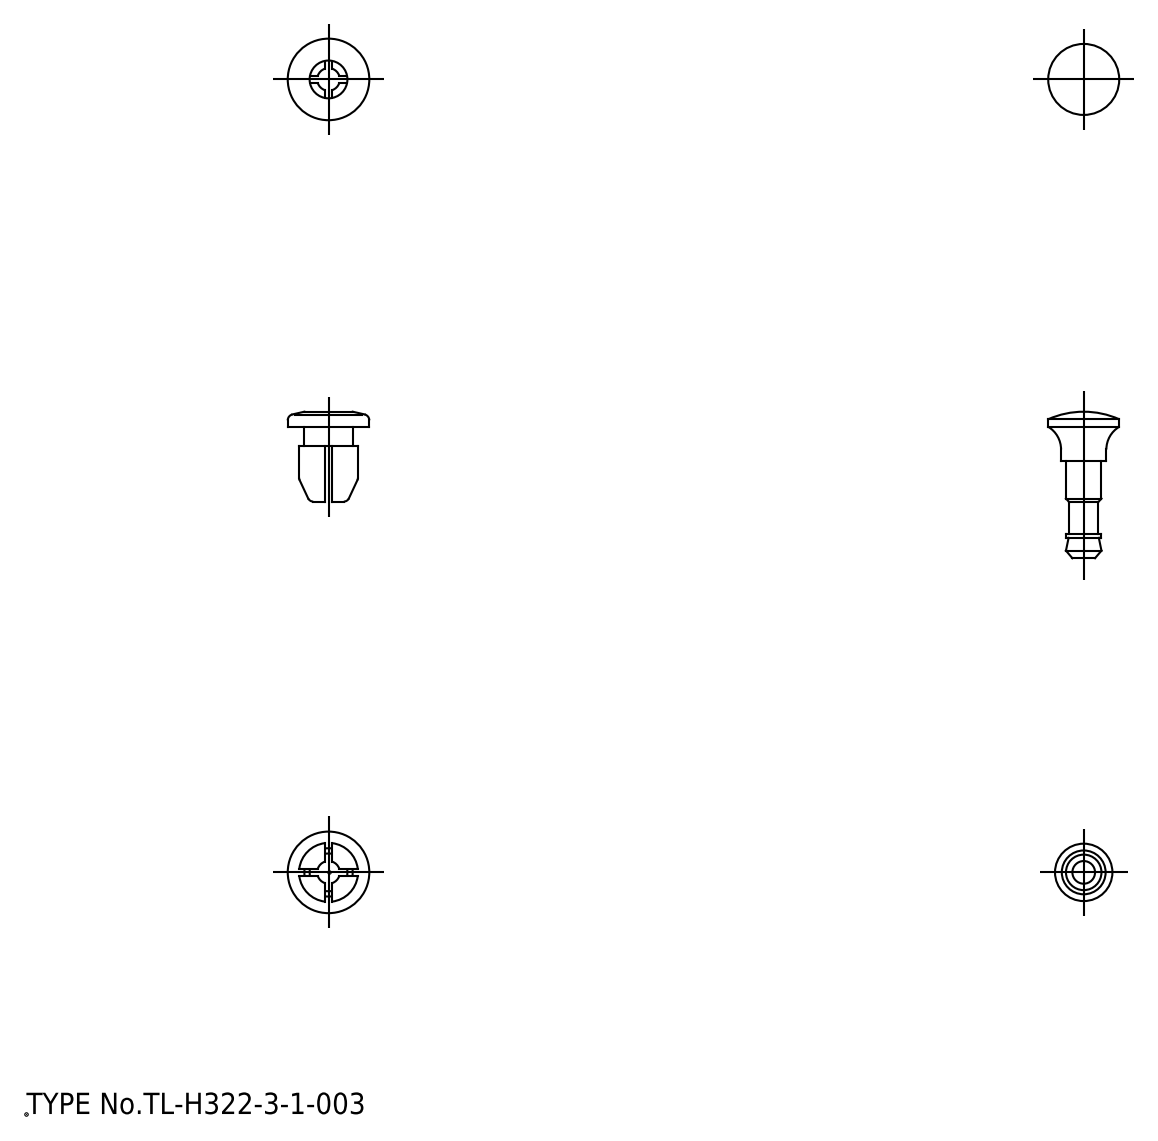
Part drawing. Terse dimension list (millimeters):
name: grommet; plunger
written by: spGate 18.9.1 (****-****-****-****) (AUTOMOTIVE_DESIGN)
unit: mm
bodies: 2 solids, 80 faces (26 planar, 24 cylindrical, 30 other)
size: 21.4 × 10.8 × 10.8
volume: 760 mm³; area: 1 046 mm²
holes: 1× ⌀5
bosses: 1× ⌀10.8, 1× ⌀9.4, 1× ⌀7.8, 1× ⌀6.4, 1× ⌀6, 1× ⌀4.7, 1× ⌀3.8
rounds: 1× R1.5
face distances: 1, 2, 2.5, 4.5, 7.5, 5, 3, 9.9, 4.7, 2.7
